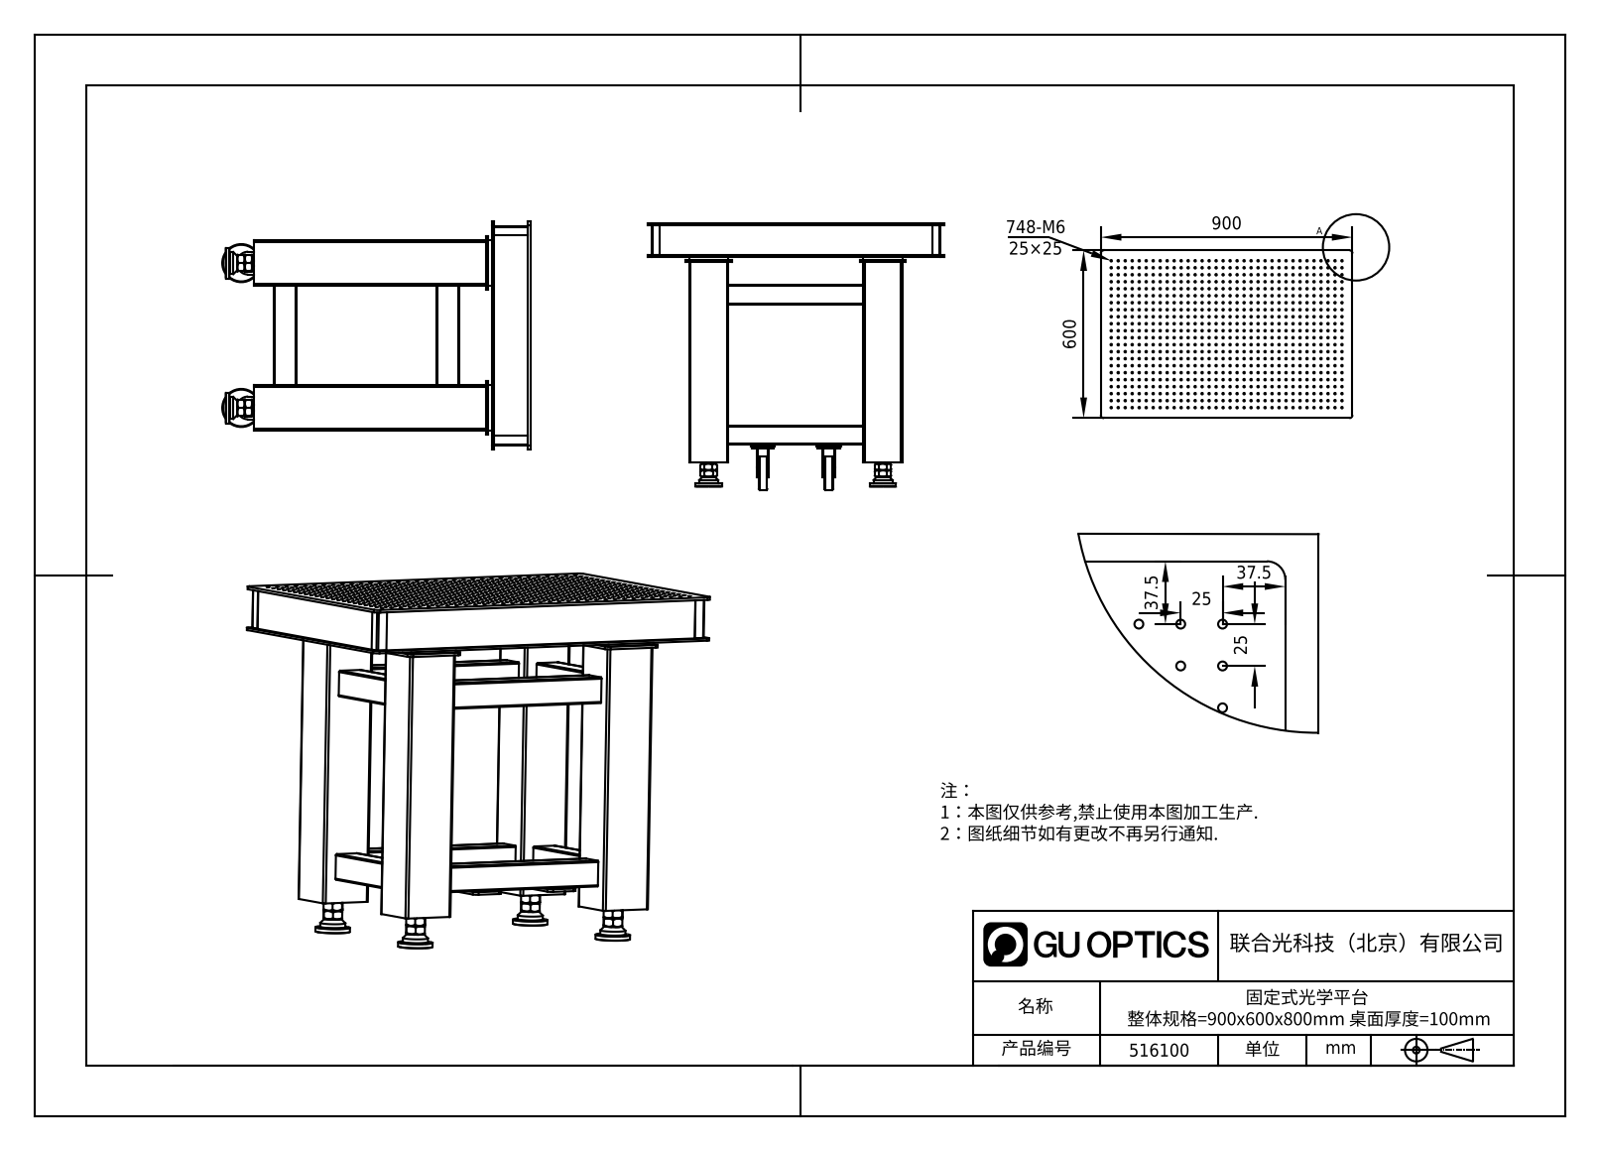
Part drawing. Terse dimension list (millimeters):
name: 516100
written by: SolidWorks 2020 (AUTOMOTIVE_DESIGN)
unit: mm
bodies: 63 solids, 2510 faces (494 planar, 1824 cylindrical, 192 other)
size: 900 × 809 × 600
volume: 59 740 000 mm³; area: 7 878 000 mm²
holes: 748× ⌀5.3, 16× ⌀8.5, 16× ⌀9, 4× ⌀17.5, 4× ⌀22, 4× ⌀28, 4× ⌀43
bosses: 4× ⌀80, 4× ⌀58, 4× ⌀14, 2× ⌀100
rounds: 48× R1, 48× R10, 36× R3, 16× R5, 16× R7, 4× R2, 4× R11, 2× R30
face distances: 90, 116, 4, 380, 6, 530, 5, 112, 95, 2
hole spacings: 380, 25, 200, 45, 78, 90.05, 147.74, 191.51
